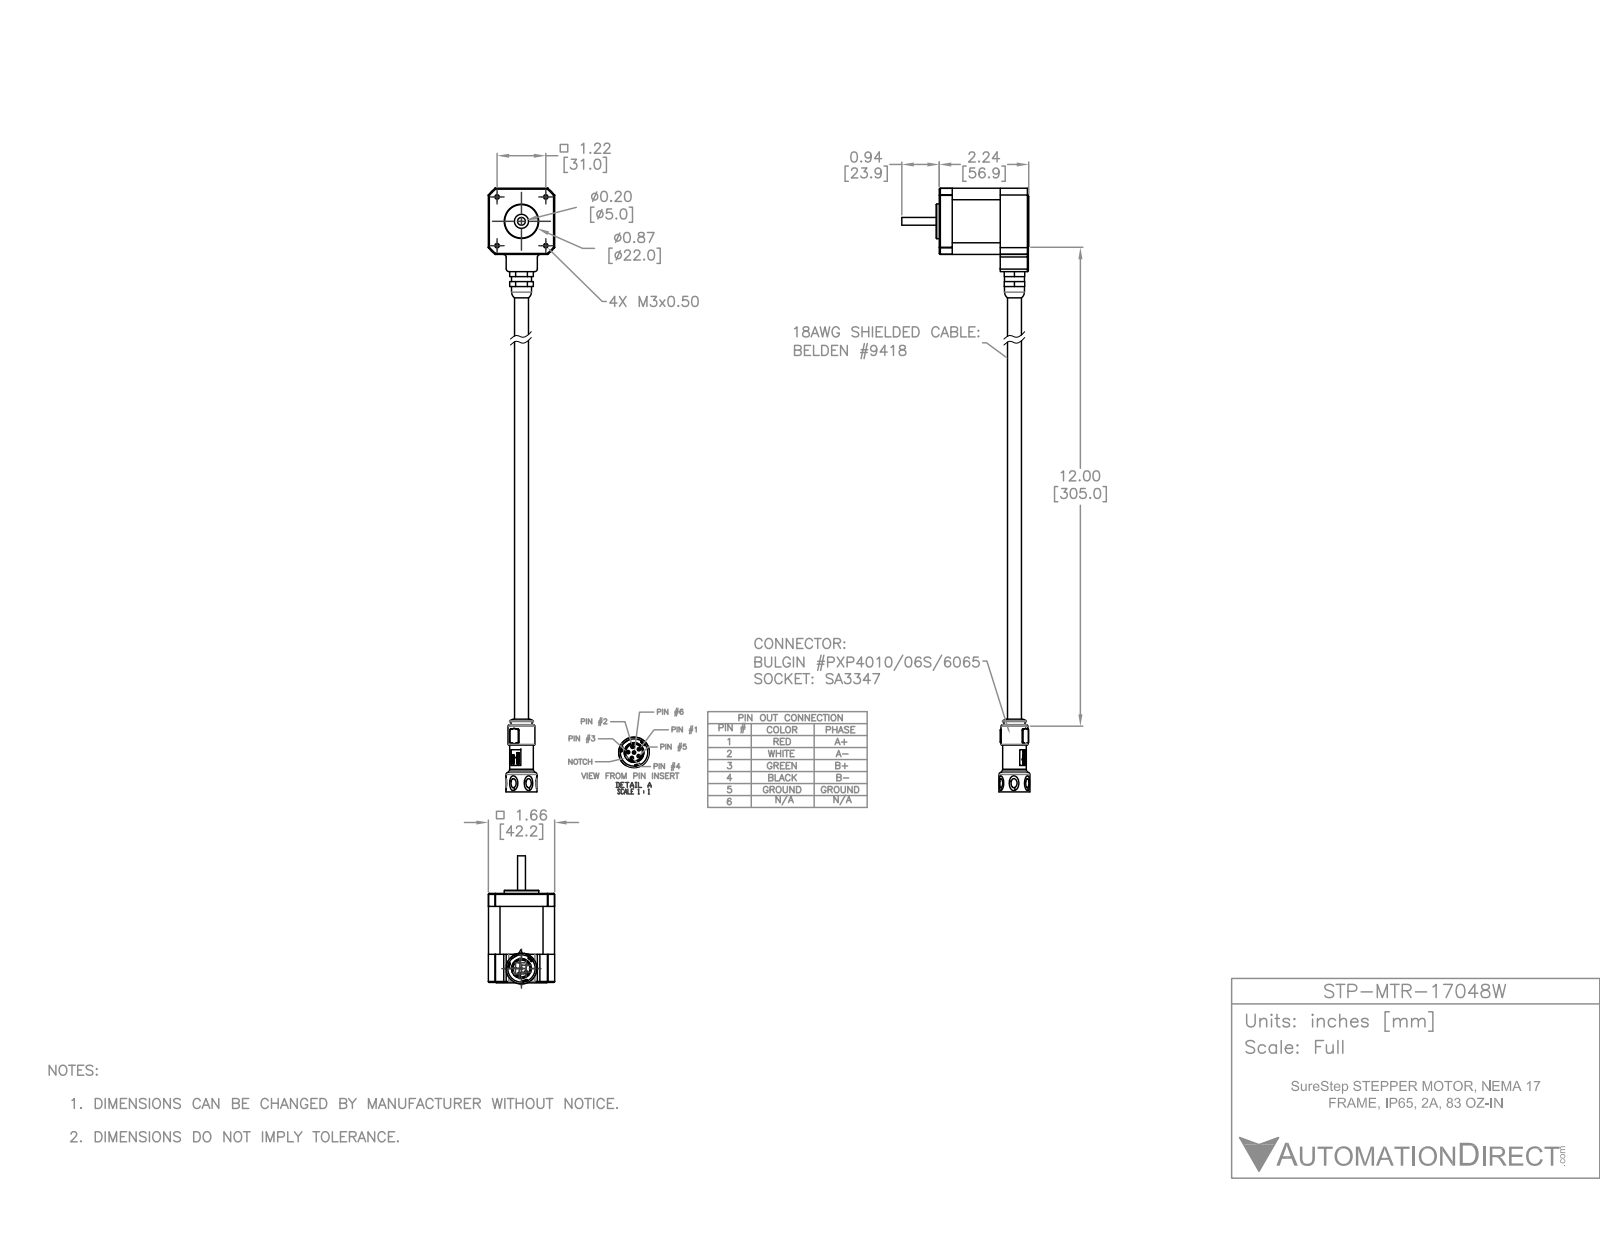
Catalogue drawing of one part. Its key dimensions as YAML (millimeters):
part_name: "STP-MTR-17048W c1"
step_written_by: "SolidWorks 2017 (AUTOMOTIVE_DESIGN)"
units: millimeters
bodies: {solids: 7, faces: 848, planar: 301, cylindrical: 237, other: 310}
overall_size: [384, 81.6, 42.2]
volume: 128700
surface_area: 30440
round_holes:
  - {diameter: 1.2, count: 6}
  - {diameter: 2.2, count: 4}
  - {diameter: 3.8, count: 4}
  - {diameter: 3.2, count: 1}
  - {diameter: 5.8, count: 1}
  - {diameter: 9, count: 1}
  - {diameter: 11.1, count: 1}
  - {diameter: 11.4, count: 1}
  - {diameter: 17.5, count: 1}
round_bosses_or_shafts:
  - {diameter: 3.3, count: 4}
  - {diameter: 1.3, count: 4}
  - {diameter: 31.8, count: 1}
  - {diameter: 22, count: 1}
  - {diameter: 19.7, count: 1}
  - {diameter: 17.1, count: 1}
  - {diameter: 15.6, count: 1}
  - {diameter: 15, count: 1}
partial_cylinders:
  - {radius: 0.1, count: 28}
  - {radius: 0.6, count: 19}
  - {radius: 0.5, count: 12}
  - {radius: 9.9, count: 6}
  - {radius: 1.6, count: 4}
  - {radius: 7.3, count: 3}
  - {radius: 2.3, count: 1}
  - {radius: 4, count: 1}
face_to_face_distances: [42.1, 42.1, 42.2, 56.6, 56.9, 10.9, 11, 53, 53.1, 58.9]
hole_center_spacings: [7.1, 3.8, 31, 21.9, 3.7, 4.4, 4.4, 43.8]
